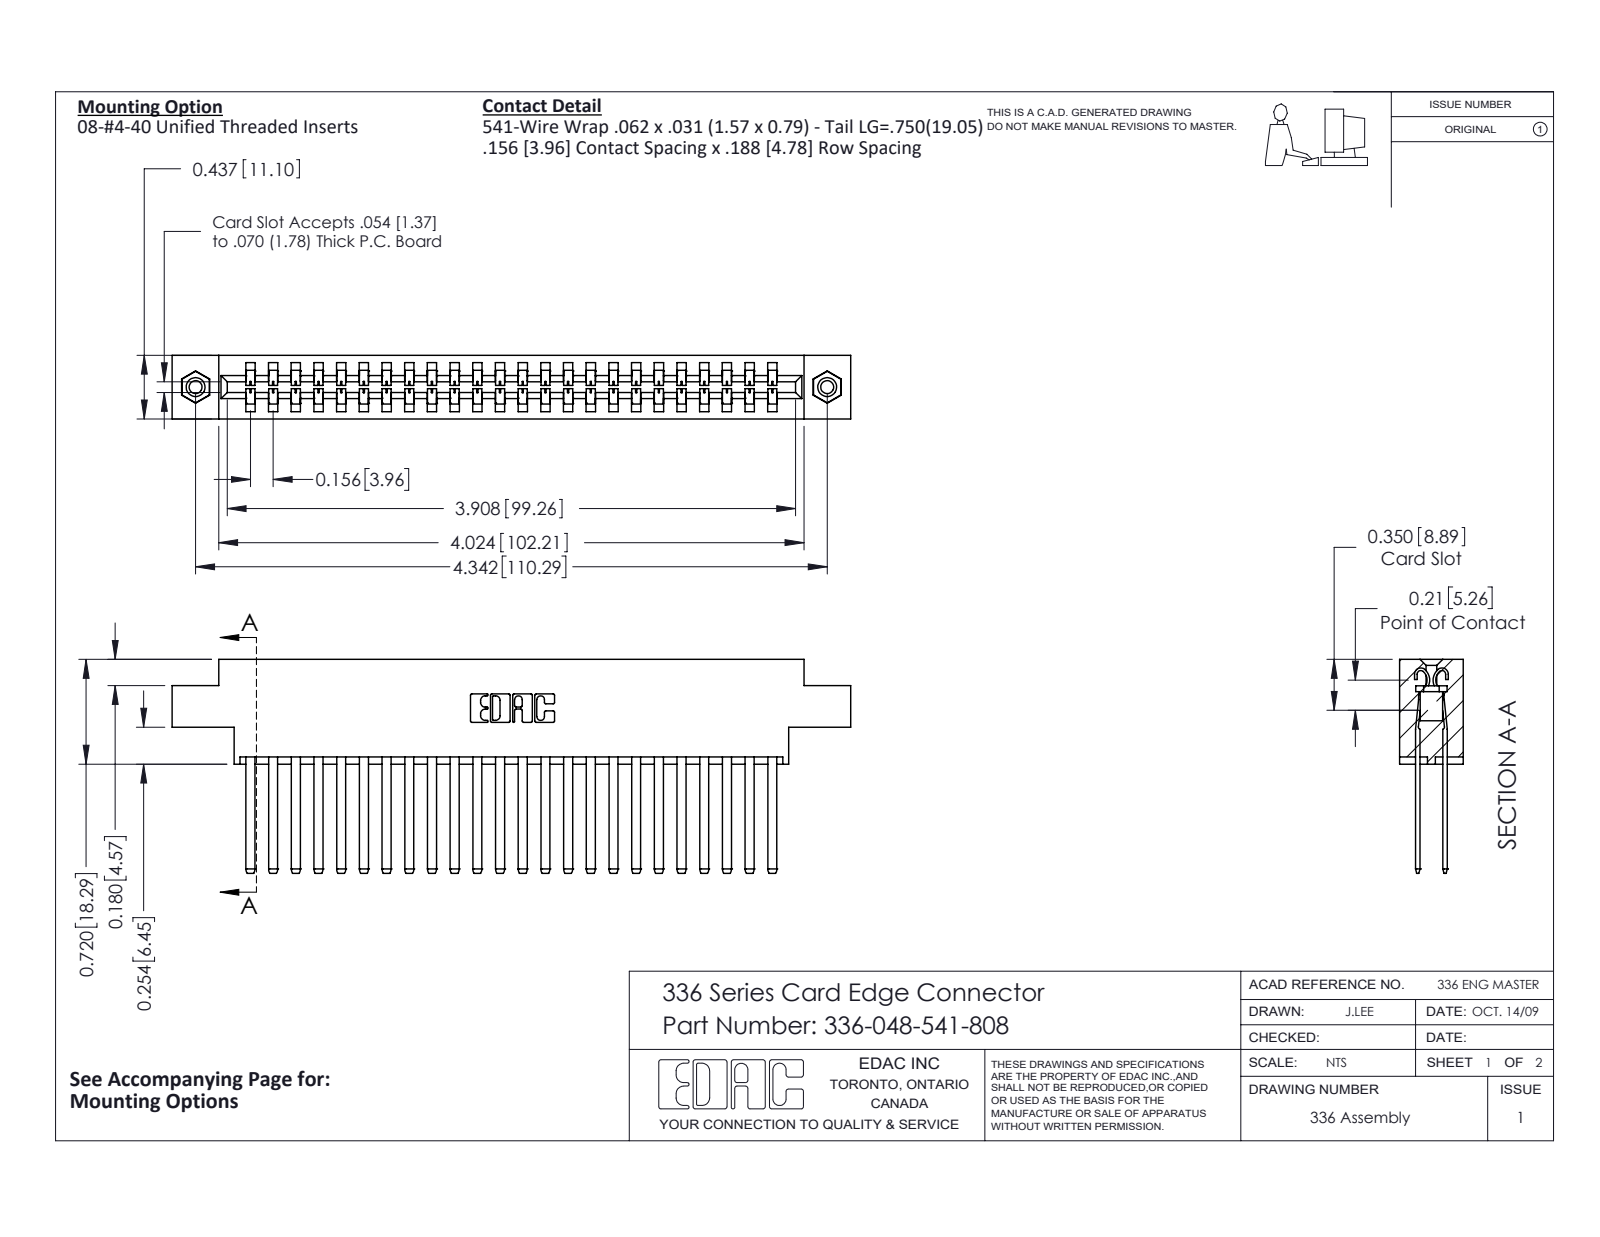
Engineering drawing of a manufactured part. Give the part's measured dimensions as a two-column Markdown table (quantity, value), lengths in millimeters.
| quantity | value |
| --- | --- |
| part name | 336 Part_Offset - .156 Dia - TI; 345-250-001_345-250-003-102; 336-048-541-808; 336-290-001_336-290-541 |
| STEP written by | SolidWorks 2020 (CONFIG_CONTROL_DESIGN) |
| units | millimeters |
| bodies | 51 solids, 2194 faces (1354 planar, 824 cylindrical, 16 other) |
| overall size | 118.5 × 37.3 × 11.1 |
| volume | 17 710 mm³ |
| surface area | 22 390 mm² |
| round holes (diameter × count) | 2.3 × 2, 3.2 × 2, 4 × 2 |
| round bosses / shafts (diameter × count) | 3.9 × 2 |
| partial cylindrical surfaces (radius × count) | 0.1 × 96, 1.4 × 48, 0.3 × 22, 0.2 × 6, 0.8 × 6, 0.6 × 4, 1 × 4, 0.7 × 3 |
| main face-to-face distances | 4.8, 8.3, 3.6, 7.5, 2.8, 0.8, 11.1, 0.8, 4.6, 4 |
| hole center spacings | 110.3 |
